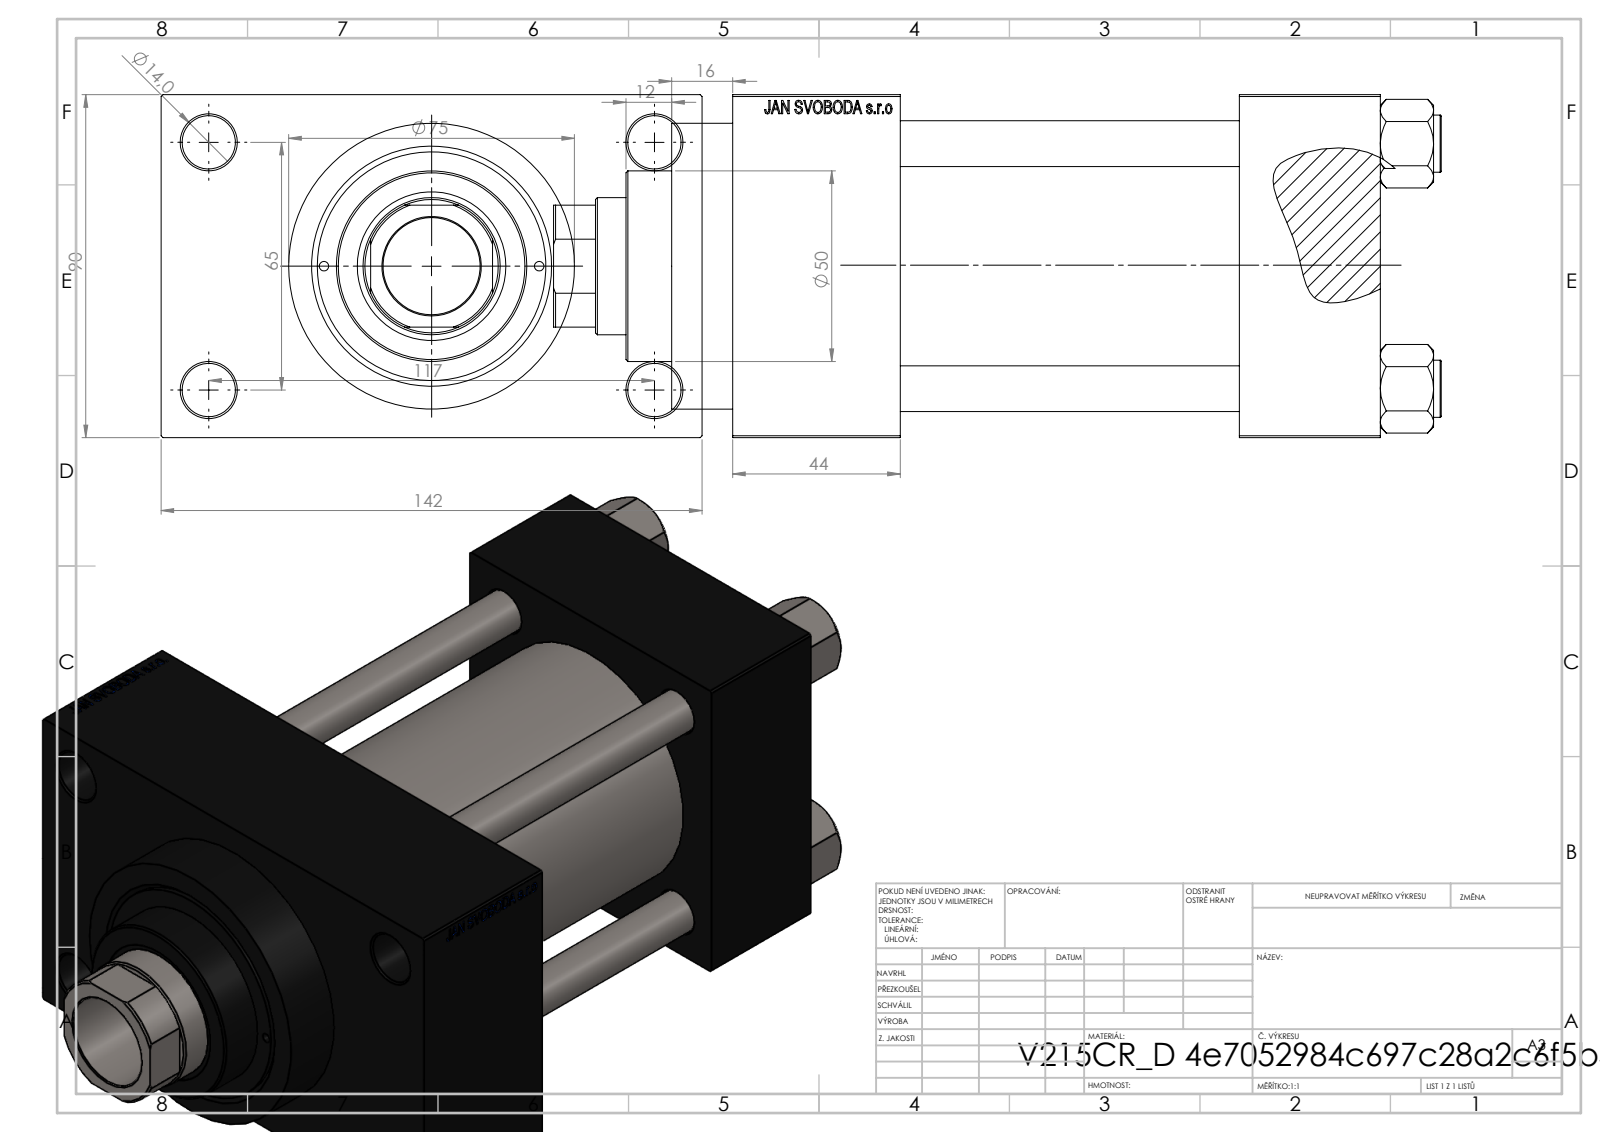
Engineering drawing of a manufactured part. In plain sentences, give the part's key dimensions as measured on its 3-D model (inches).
The part is named "V215CR_VCP_D; NUT_M5_D; V215CR_D_TYCINKA; V215_VC_A (+1 more)". Its 3-D file was written by "SolidWorks 2019 (CONFIG_CONTROL_DESIGN)". It is 11 solids with 1111 faces: 499 planar, 92 cylindrical and 520 other. Overall it measures 9.173 by 5.591 by 3.543 inches. Its volume is 71.64 cubic inches and its surface area 350.4 square inches. Round holes: 4 of diameter 0.472, 4 of diameter 0.551, 2 of diameter 0.098, 2 of diameter 0.276, 2 of diameter 0.825, 2 of diameter 1.181, 1 of diameter 1.004, 1 of diameter 1.417, 1 of diameter 1.535, 1 of diameter 1.969, 1 of diameter 2.362, 1 of diameter 2.48. Round bosses or shafts: 4 of diameter 0.591, 1 of diameter 2.953, 1 of diameter 2.717. Partial cylindrical surfaces (rounded edges, fillets, slot ends): 1 of radius 0.689. The main face-to-face distances are 3.543, 3.504, 1.457, 4.961, 6.693, 5.236, 1.732, 1.024, 4.567, 5.591. The hole center spacings are 1.037, 1.275, 1.748, 1.79, 2.531, 2.635, 2.694, 2.748.
